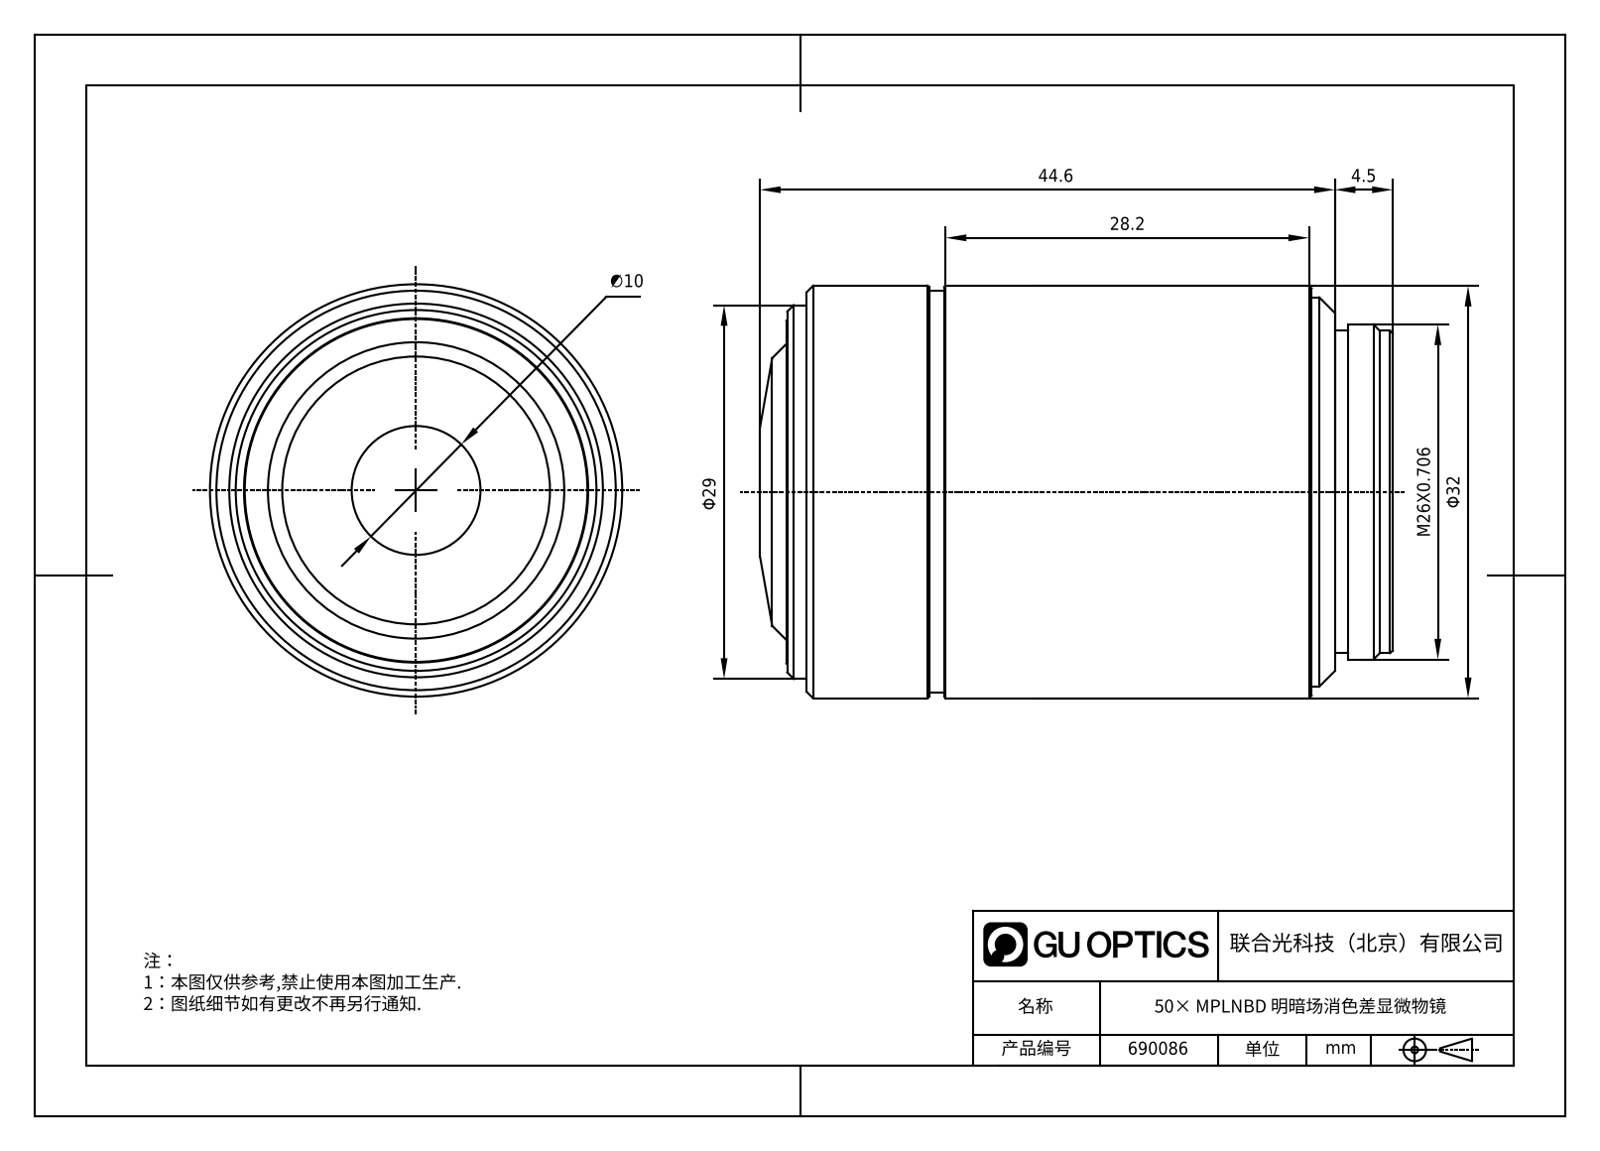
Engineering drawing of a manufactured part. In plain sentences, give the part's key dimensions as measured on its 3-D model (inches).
The part is named "690086.stp; MPLN50XBD.stp; 690086". Its 3-D file was written by "SolidWorks 2020 (CONFIG_CONTROL_DESIGN)". It is 1 solid with 48 faces: 10 planar, 16 cylindrical and 22 other. Overall it measures 1.934 by 1.26 by 1.26 inches. Its volume is 2.233 cubic inches and its surface area 9.657 square inches. Round bosses or shafts: 1 of diameter 1.26, 1 of diameter 1.228, 1 of diameter 1.189, 1 of diameter 1.142, 1 of diameter 1.024, 1 of diameter 0.984. The main face-to-face distances are 1.853, 1.676, 0.177, 0.061, 1.614, 1.791, 0.081, 0.143, 1.757, 1.934.
